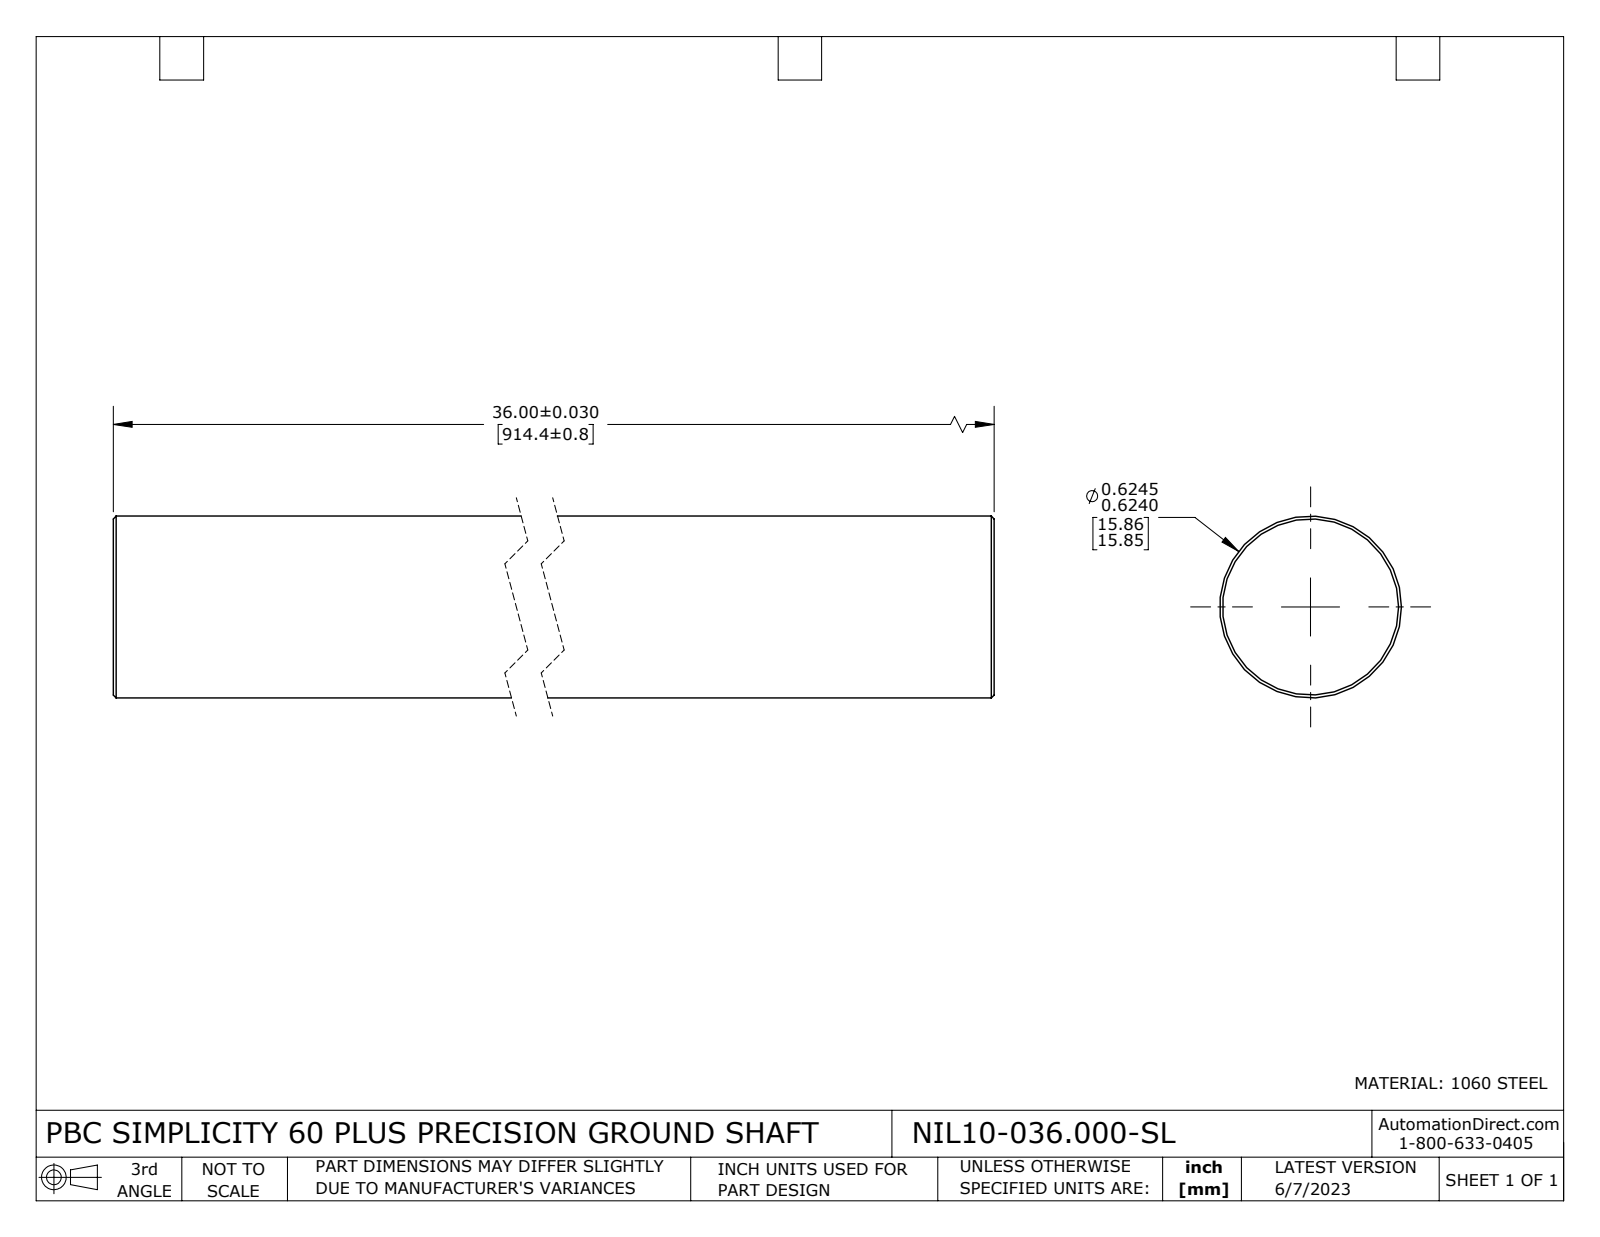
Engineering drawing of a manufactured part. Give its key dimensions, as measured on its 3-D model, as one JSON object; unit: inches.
{"part_name": "NIL10-036.000-SL", "step_written_by": "SolidWorks 2021 (CONFIG_CONTROL_DESIGN)", "units": "inches", "bodies": {"solids": 1, "faces": 8, "planar": 2, "cylindrical": 2, "other": 4}, "overall_size": [36, 0.625, 0.625], "volume_in3": 11.04, "surface_area_in2": 71.28, "round_bosses_or_shafts": [[0.625, 1]], "face_to_face_distances": [36]}
